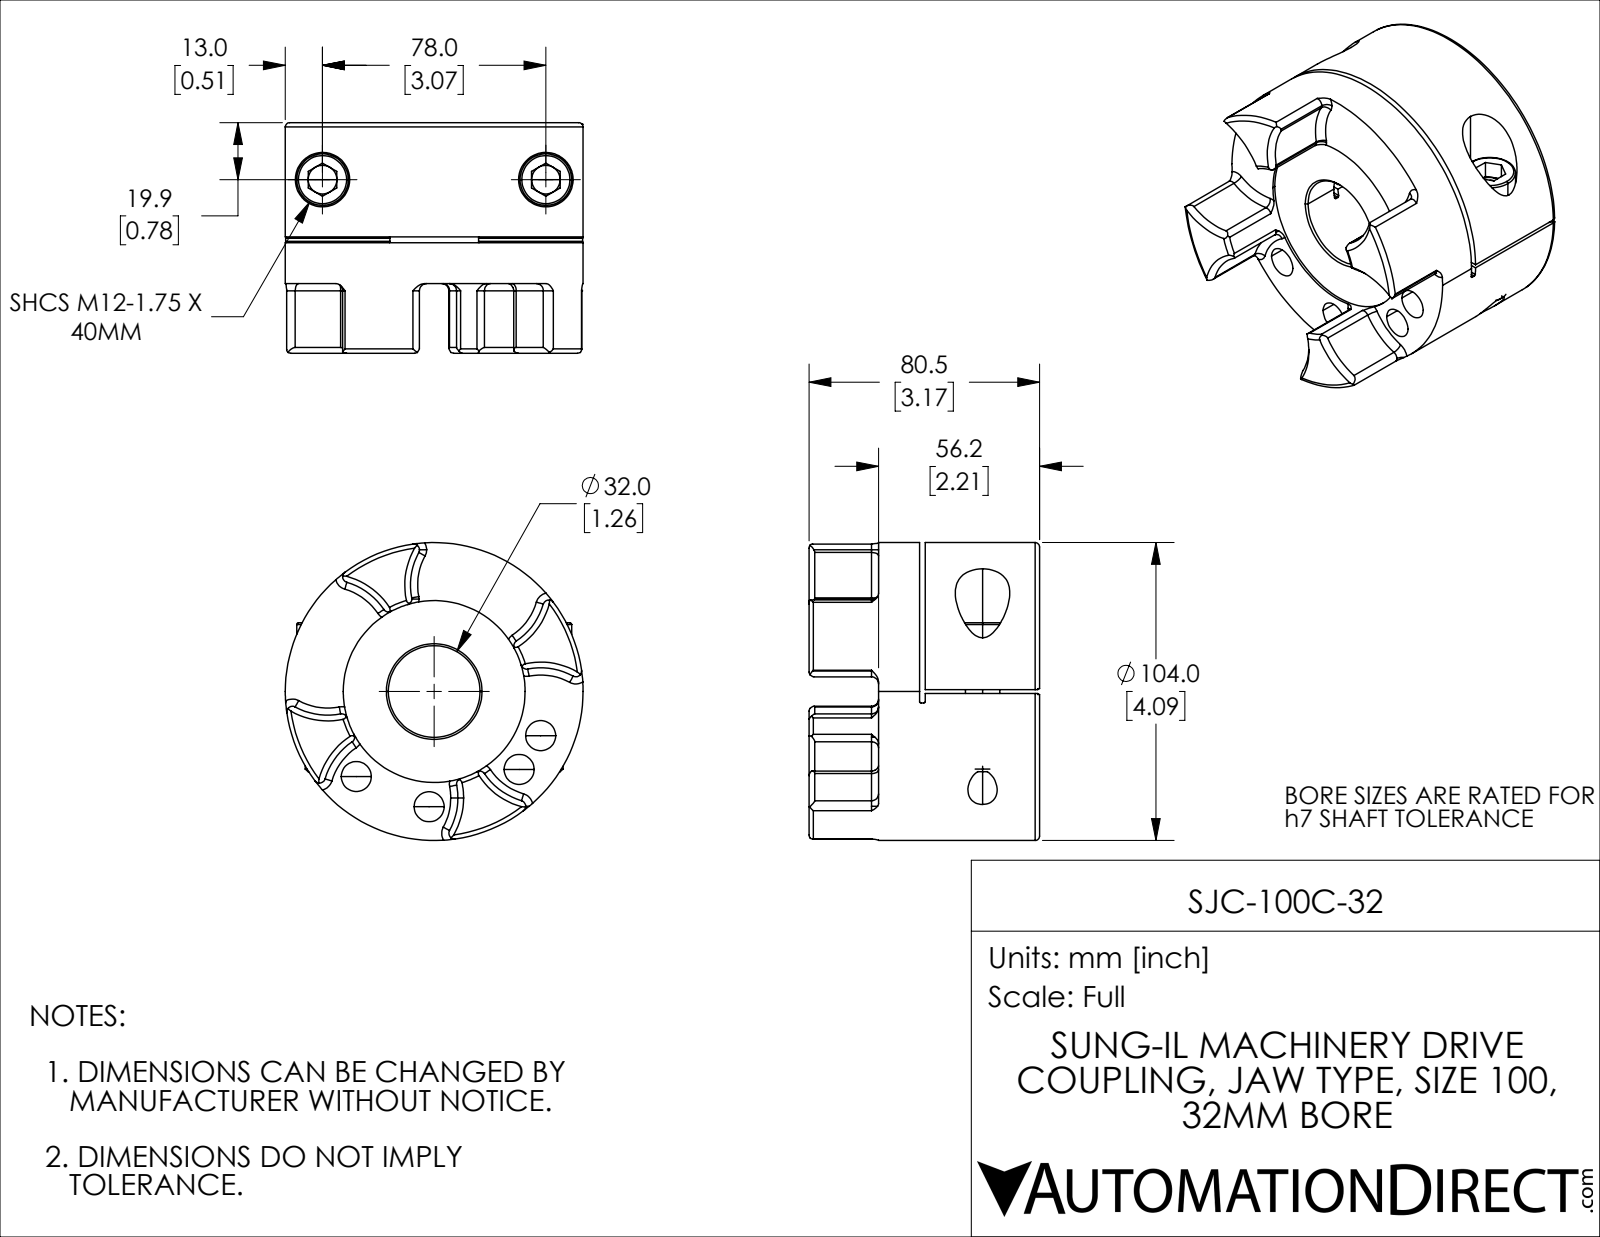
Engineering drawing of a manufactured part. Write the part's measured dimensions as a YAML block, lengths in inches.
part_name: "SJC-100C-32"
step_written_by: "SolidWorks 2021 (CONFIG_CONTROL_DESIGN)"
units: inches
bodies: {solids: 4, faces: 222, planar: 55, cylindrical: 82, other: 85}
overall_size: [4.094, 4.094, 3.169]
volume: 26.72
surface_area: 112.3
round_holes:
  - {diameter: 0.413, count: 4}
  - {diameter: 0.394, count: 2}
  - {diameter: 0.402, count: 2}
  - {diameter: 0.492, count: 2}
  - {diameter: 0.748, count: 2}
  - {diameter: 1.26, count: 1}
  - {diameter: 2.5, count: 1}
round_bosses_or_shafts:
  - {diameter: 0.709, count: 2}
  - {diameter: 0.472, count: 2}
  - {diameter: 4.094, count: 1}
partial_cylinders:
  - {radius: 0.079, count: 16}
  - {radius: 0.932, count: 4}
  - {radius: 0.02, count: 2}
  - {radius: 2.953, count: 1}
face_to_face_distances: [0.079, 1.65, 1.571, 2.213, 0.642, 0.563, 2.177, 0.606, 0.528, 0.035]
hole_center_spacings: [1.585, 0.55, 1.083, 1.34, 1.818, 2.241, 2.596, 3.071]
